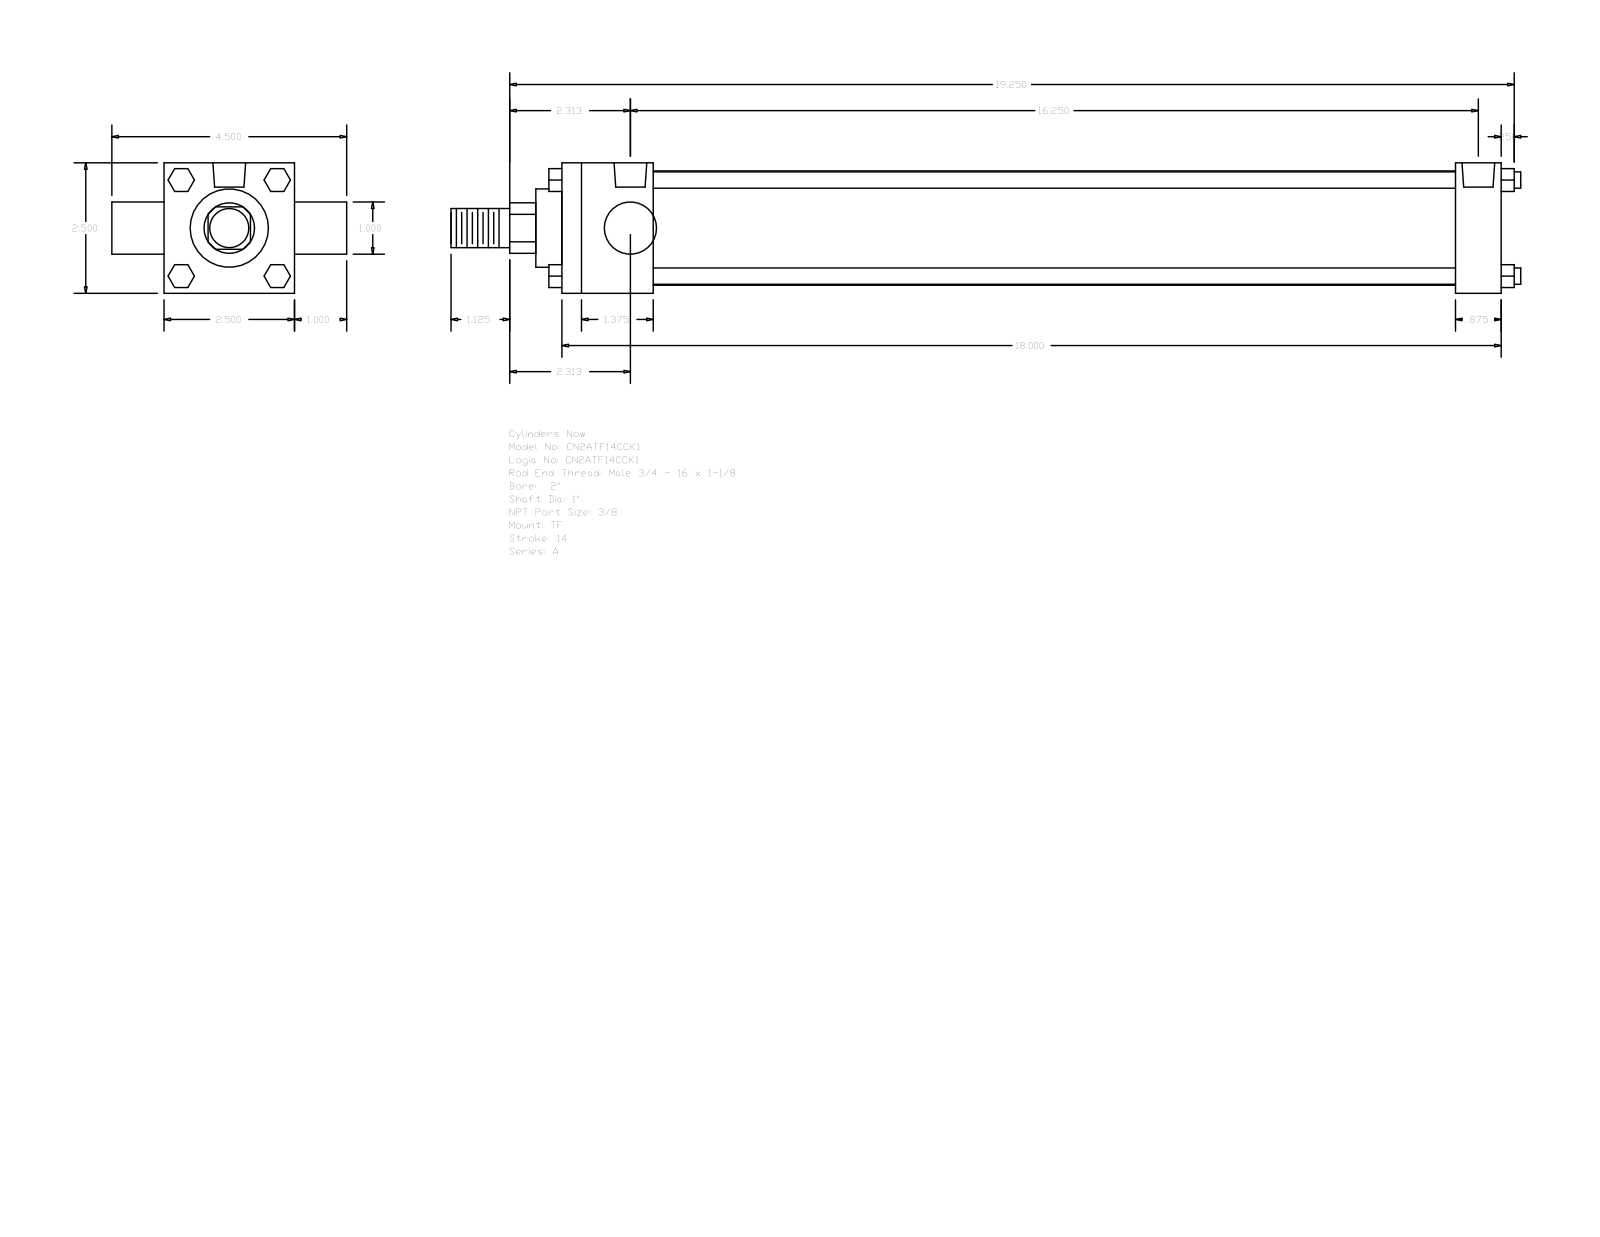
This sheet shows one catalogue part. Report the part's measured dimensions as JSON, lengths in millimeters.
{"part_name": "A_TF__0200_1", "step_written_by": "GSSL Pune (CONFIG_CONTROL_DESIGN)", "units": "millimeters", "bodies": {"solids": 0, "faces": 120, "planar": 92, "cylindrical": 28, "other": 0}, "overall_size": [520.7, 114.3, 63.5], "round_holes": [[5.56, 3], [15.93, 2]], "round_bosses_or_shafts": [[7.94, 4], [25.4, 2], [55.63, 1], [38.1, 1], [19.05, 1]], "partial_cylinders_radius": [[12.29, 1]], "face_to_face_distances": [63.5, 457.2, 44.45, 434.98, 390.53, 412.75, 22.22, 25.4, 88.9, 469.9], "hole_center_spacings": [1.59, 3.98, 407.18, 408.77, 411.16, 412.75]}
